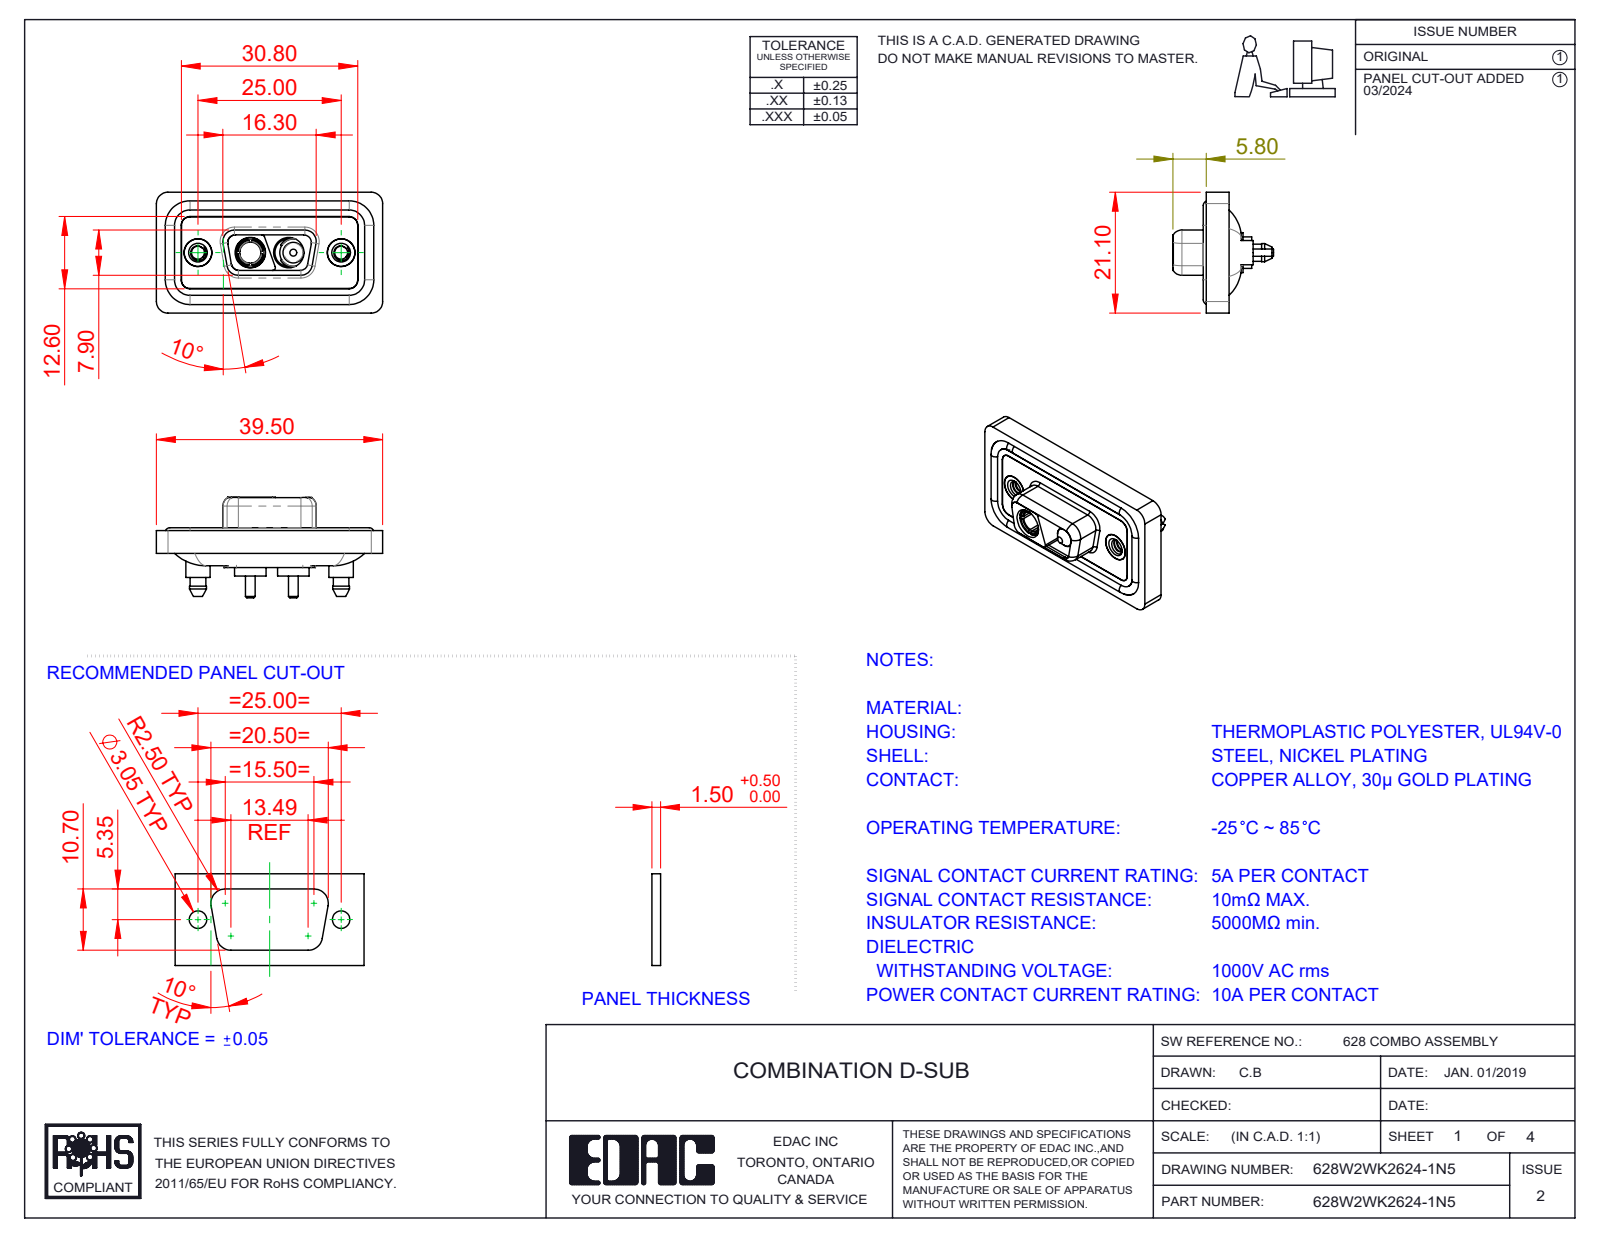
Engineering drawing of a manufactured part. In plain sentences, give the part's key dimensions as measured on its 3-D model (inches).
The part is named "628Combo Shell Front_09 Contacts; 628Combo Waterproof Housing_09 Contacts; 628Combo Threaded Boardlock_5; Power Pin_10A S (+4 more)". Its 3-D file was written by "SolidWorks 2023 (CONFIG_CONTROL_DESIGN)". It is 11 solids with 550 faces: 160 planar, 263 cylindrical and 127 other. Overall it measures 1.555 by 0.831 by 0.691 inches. Its volume is 0.287 cubic inches and its surface area 11.86 square inches. Round holes: 4 of diameter 0.191, 2 of diameter 0.089, 2 of diameter 0.157, 2 of diameter 0.159, 2 of diameter 0.197, 2 of diameter 0.209, 1 of diameter 0.146. Round bosses or shafts: 4 of diameter 0.063, 2 of diameter 0.217, 2 of diameter 0.213, 2 of diameter 0.205, 2 of diameter 0.195, 2 of diameter 0.189, 2 of diameter 0.187, 2 of diameter 0.167. Partial cylindrical surfaces (rounded edges, fillets, slot ends): 24 of radius 0.059, 18 of radius 0.079, 10 of radius 0.063, 8 of radius 0.053, 6 of radius 0.02, 4 of radius 0.01, 4 of radius 0.024, 4 of radius 0.026. The main face-to-face distances are 0.016, 0.043, 0.114, 0.063, 0.02, 0.071, 0.222, 0.059, 0.157, 0.211. The hole center spacings are 0.36, 0.624, 0.265, 0.984.
